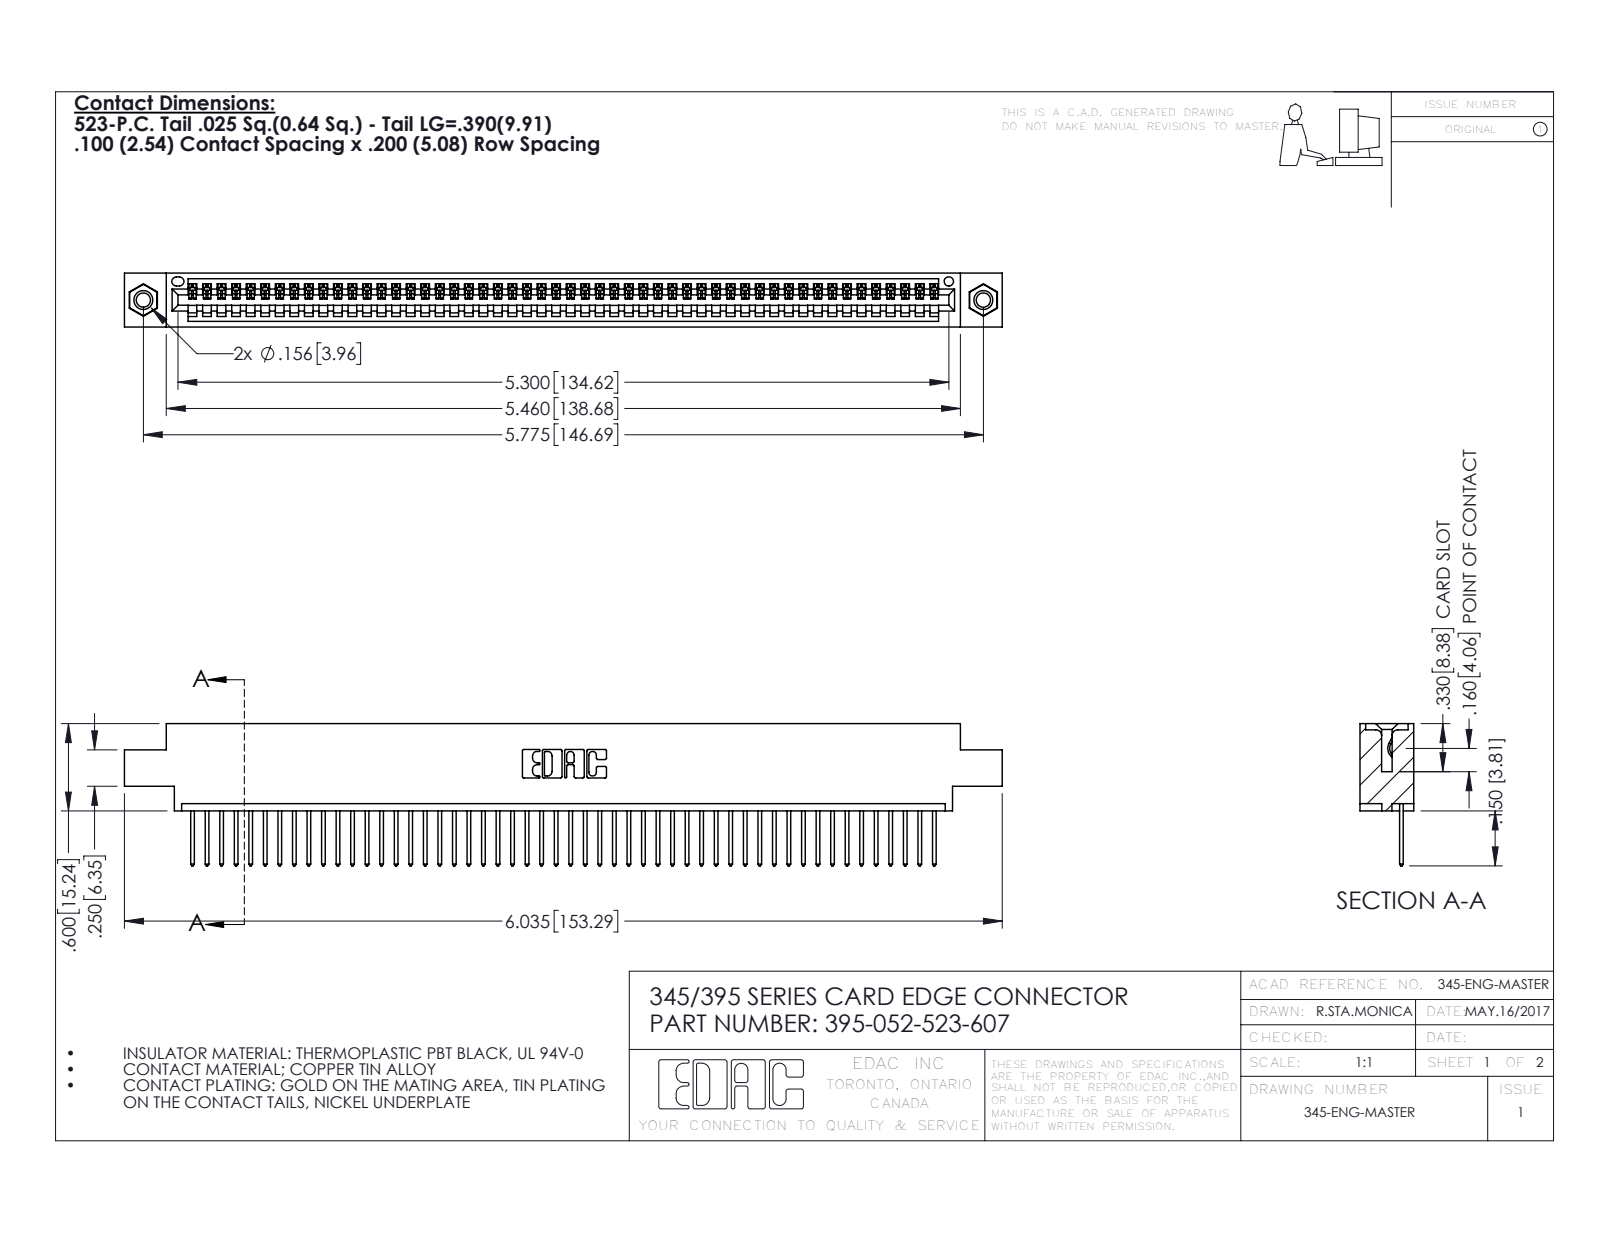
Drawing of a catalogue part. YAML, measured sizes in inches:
part_name: "395-052-523-607; 345-292-001_345-293-123; 345 Part_0.170 Offset - 0.156 Dia-TI; 345-250-001_345-250-005-103"
step_written_by: "SolidWorks 2016 (CONFIG_CONTROL_DESIGN)"
units: inches
bodies: {solids: 55, faces: 3206, planar: 2196, cylindrical: 994, other: 16}
overall_size: [6.035, 0.977, 0.37]
volume: 0.885
surface_area: 30.4
round_holes:
  - {diameter: 0.098, count: 2}
  - {diameter: 0.125, count: 2}
  - {diameter: 0.156, count: 2}
  - {diameter: 0.064, count: 1}
round_bosses_or_shafts:
  - {diameter: 0.155, count: 2}
partial_cylinders:
  - {radius: 0.006, count: 104}
  - {radius: 0.01, count: 104}
  - {radius: 0.01, count: 22}
  - {radius: 0.007, count: 6}
  - {radius: 0.031, count: 6}
  - {radius: 0.026, count: 3}
  - {radius: 0.031, count: 2}
  - {radius: 0.04, count: 2}
face_to_face_distances: [0.072, 0.298, 0.37, 0.098, 0.272, 0.025, 0.2, 0.225, 0.175, 0.149]
hole_center_spacings: [0.27, 5.539, 5.775]
